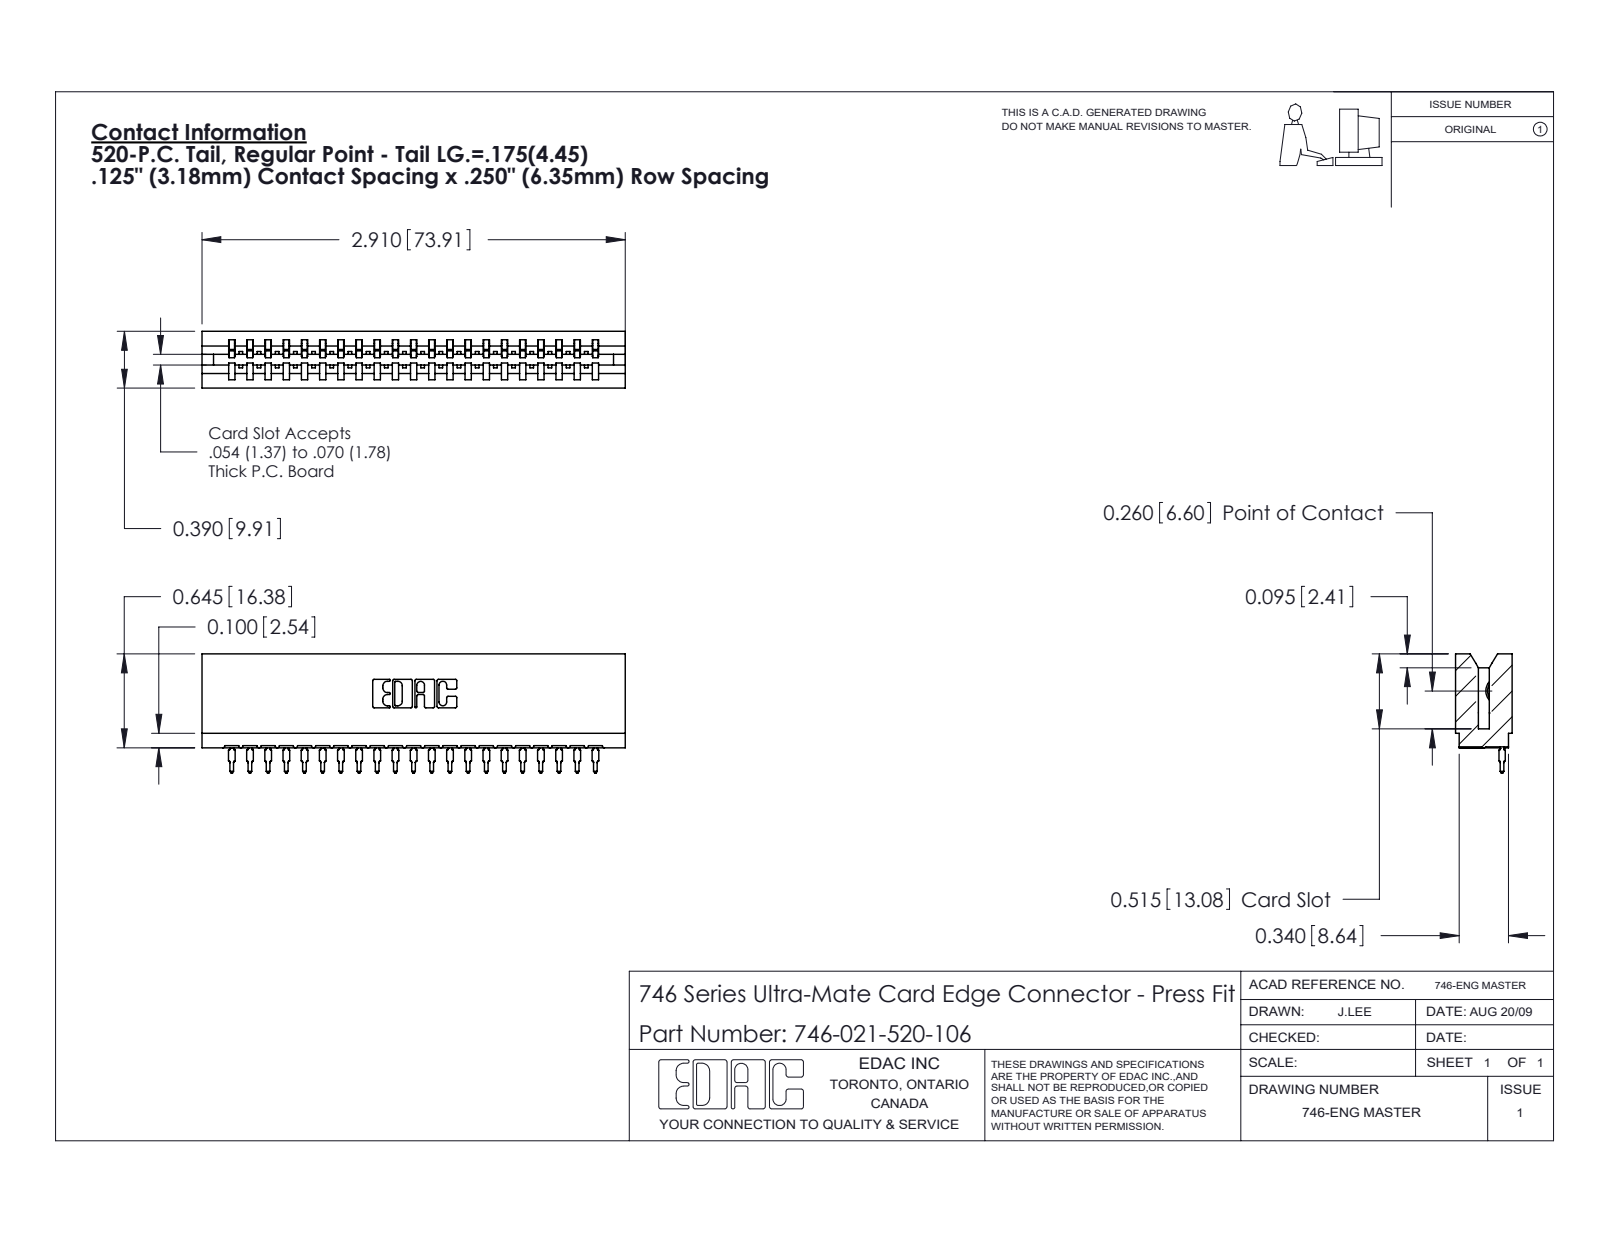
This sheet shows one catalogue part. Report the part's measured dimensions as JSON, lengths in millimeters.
{"part_name": "746 Part_.515 Slot Depth - 06; 746-021-520-106; 746-292-001_520", "step_written_by": "SolidWorks 2020 (CONFIG_CONTROL_DESIGN)", "units": "millimeters", "bodies": {"solids": 22, "faces": 2366, "planar": 1379, "cylindrical": 441, "other": 546}, "overall_size": [73.9, 20.8, 9.9], "volume_mm3": 7820, "surface_area_mm2": 11100, "partial_cylinders_radius": [[0.5, 42], [0.3, 22], [0.4, 22], [0.2, 6], [0.8, 6], [0.1, 4], [0.3, 4], [0.7, 3]], "face_to_face_distances": [1.4, 8.5, 6.4, 9.9, 12.7, 0.6, 7.8, 1.1, 3.2, 9.5]}
